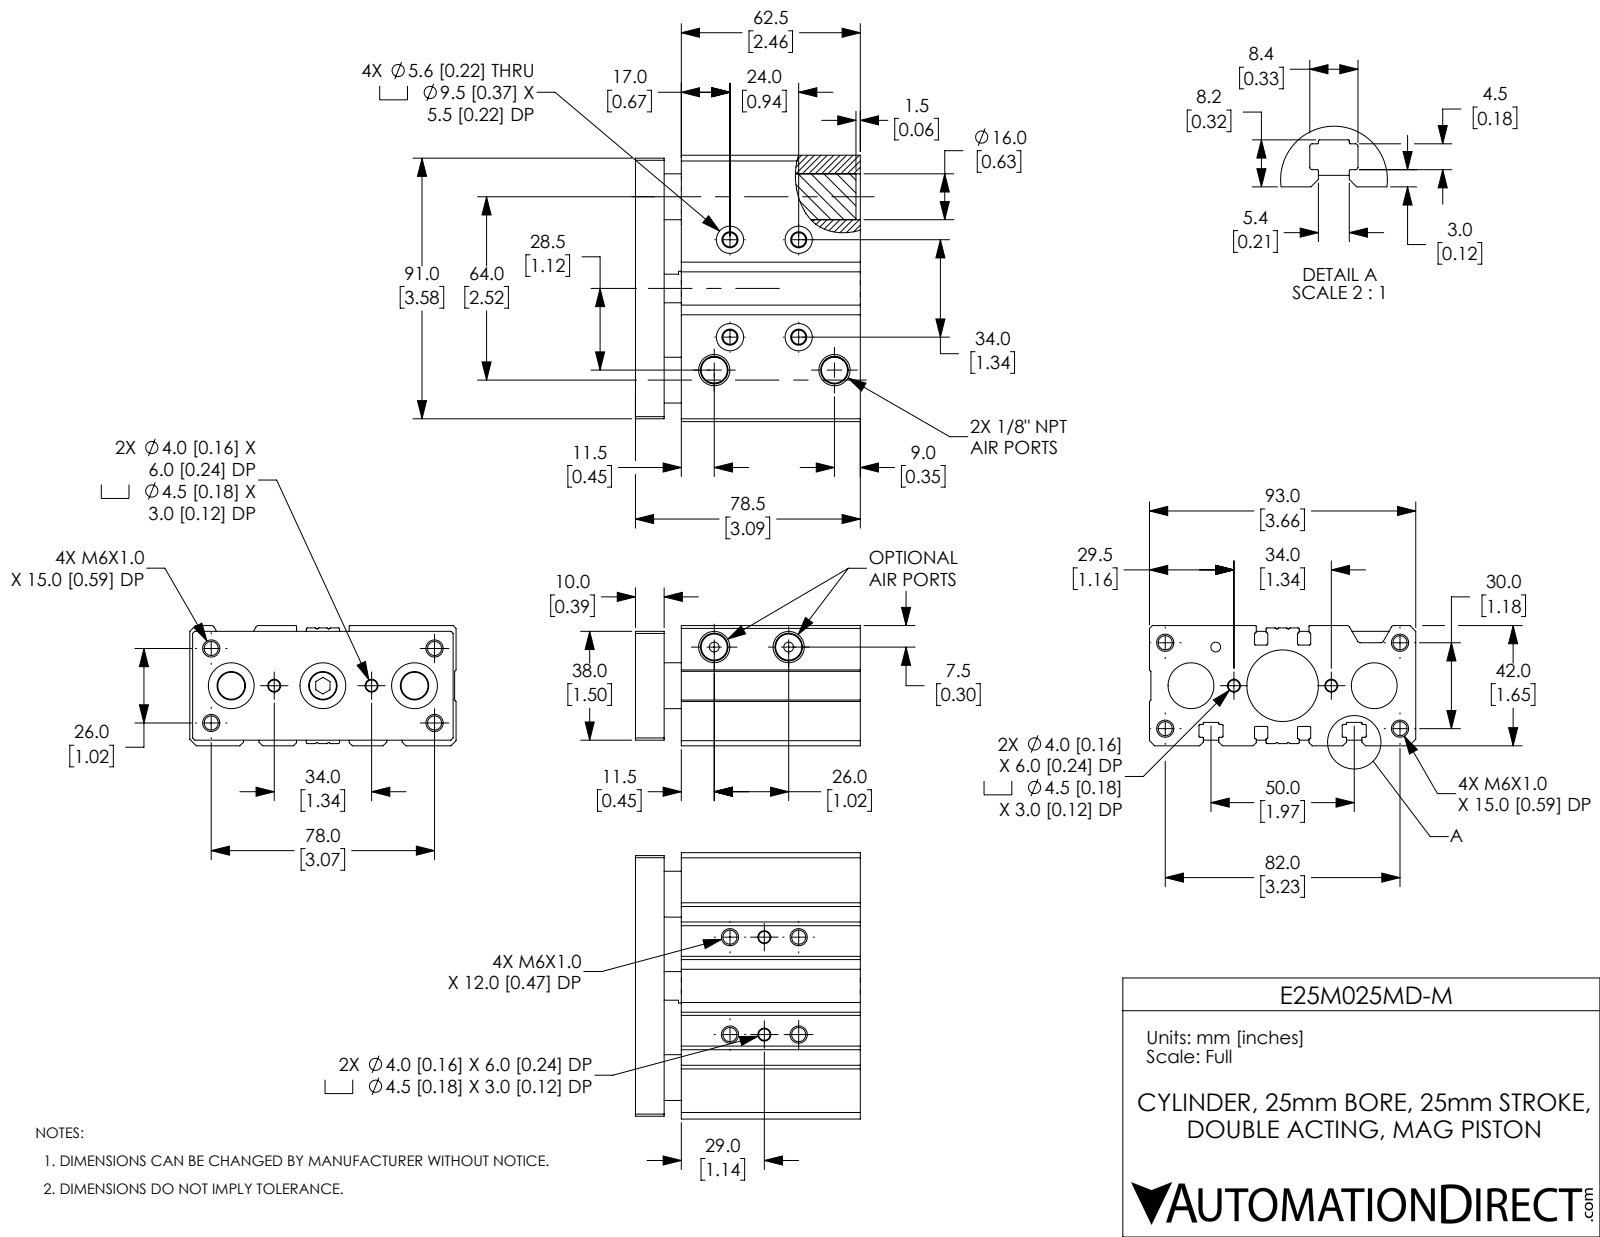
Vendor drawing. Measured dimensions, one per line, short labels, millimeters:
name: E25M025MD-M_ENDPLATE; E25M025MD-M_BODY; E25M025MD-M
written by: SolidWorks 2019 (CONFIG_CONTROL_DESIGN)
unit: mm
bodies: 5 solids, 423 faces (139 planar, 190 cylindrical, 94 other)
size: 93 × 78.5 × 42
volume: 237 967 mm³; area: 70 529 mm²
holes: 8× ⌀4.92, 4× ⌀4, 4× ⌀4.5, 4× ⌀4.92, 4× ⌀5.6, 4× ⌀9.5, 3× ⌀3.43, 3× ⌀8, 3× ⌀16, 2× ⌀9.91, 1× ⌀16, 1× ⌀25
bosses: 1× ⌀12, 1× ⌀9.91
rounds: 32× R0.2, 28× R0.4, 4× R1, 2× R0.3
face distances: 6, 42, 16, 10, 2, 78.5, 68.5, 62.5, 40, 8
hole spacings: 2.83, 12, 14.76, 17.49, 25.55, 28.07, 28.3, 34
